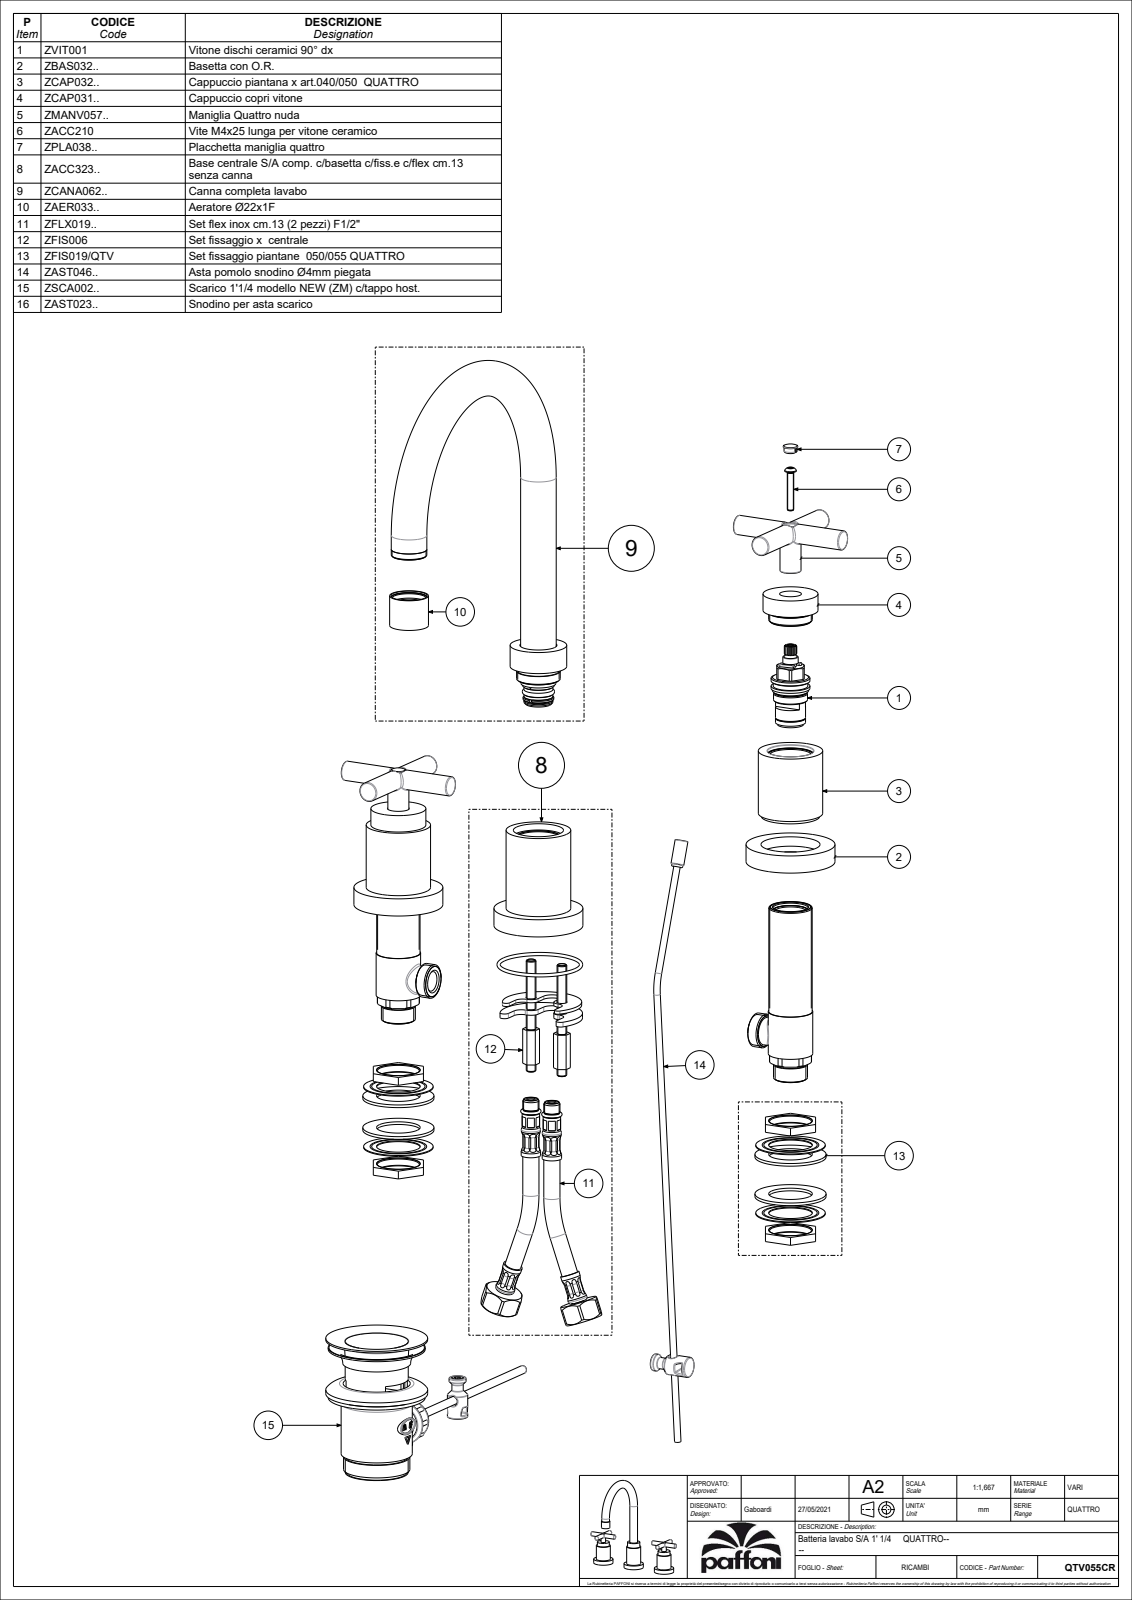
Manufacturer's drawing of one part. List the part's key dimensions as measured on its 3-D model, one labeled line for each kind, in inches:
Part name (STEP PRODUCT): QTV055CR
STEP written by: CREO PARAMETRIC BY PTC INC, 2020044 (CONFIG_CONTROL_DESIGN)
Units: inches
Bodies: 9 solids, 2474 faces (1914 planar, 334 cylindrical, 226 other)
Overall size (bounding box): 10.827 × 10.677 × 8.313
Volume: 18.49 in³ · Surface area: 230.8 in²
Round holes (diameter × count): ⌀0.748 ×4, ⌀0.276 ×3, ⌀0.787 ×3, ⌀1.004 ×3, ⌀1.437 ×3, ⌀1.85 ×3, ⌀2.087 ×3, ⌀0.13 ×2, ⌀0.177 ×2, ⌀0.207 ×2, ⌀0.315 ×2, ⌀0.346 ×2
Round bosses / shafts (diameter × count): ⌀2.165 ×3, ⌀1.929 ×3, ⌀1.417 ×3, ⌀0.945 ×3, ⌀0.472 ×3, ⌀1.772 ×2, ⌀1.567 ×2, ⌀1.339 ×2
Partial cylindrical surfaces — rounded edges, fillets, slot ends (radius × count): R0.004 ×34, R0.02 ×4, R0.039 ×4, R0.118 ×2, R0.37 ×2
Main face-to-face distances: 0.433, 0.087, 0.346, 0.079, 0.354, 0.268, 2.421, 2.335, 2.067, 1.988
Hole centre spacings: 0.355, 0.585, 0.606, 0.938, 3.526, 3.647, 3.937, 4.237
